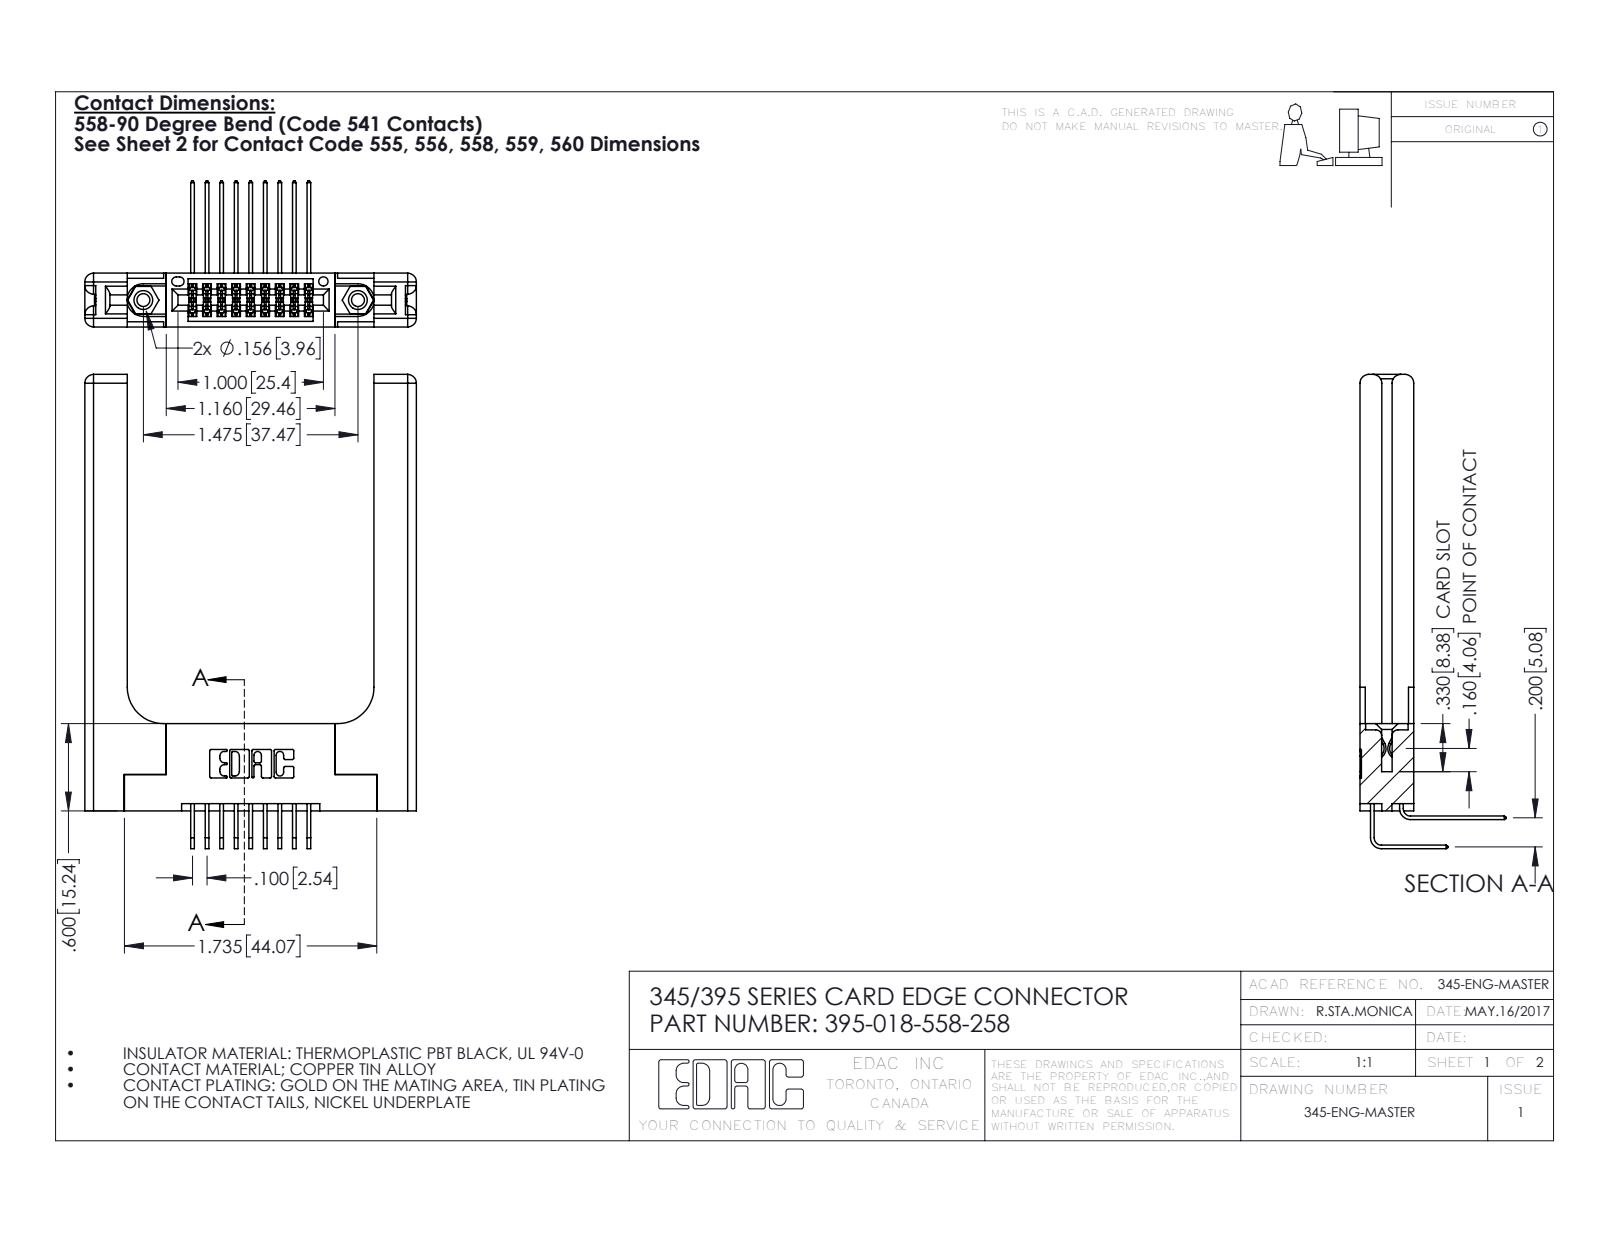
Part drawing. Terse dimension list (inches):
name: 345 Part_Flush Mounting Lugs - 0.156 Dia-TH; 345-292-001_558 Tail - 2; 345-220-058_345-220-058; 395-018-558-258 (+2 more)
written by: SolidWorks 2016 (CONFIG_CONTROL_DESIGN)
unit: in
bodies: 23 solids, 1318 faces (858 planar, 400 cylindrical, 60 other)
size: 3.259 × 2.279 × 1.005
volume: 0.848 in³; area: 20.03 in²
holes: 2× ⌀0.089, 2× ⌀0.125, 2× ⌀0.156, 1× ⌀0.064
bosses: 2× ⌀0.155
rounds: 28× R0.006, 22× R0.01, 16× R0.06, 6× R0.007, 6× R0.031, 3× R0.026, 2× R0.014, 2× R0.019
face distances: 0.37, 0.072, 0.15, 0.22, 0.077, 0.148, 0.298, 0.2, 1.696, 0.225
hole spacings: 0.27, 1.244, 1.475
